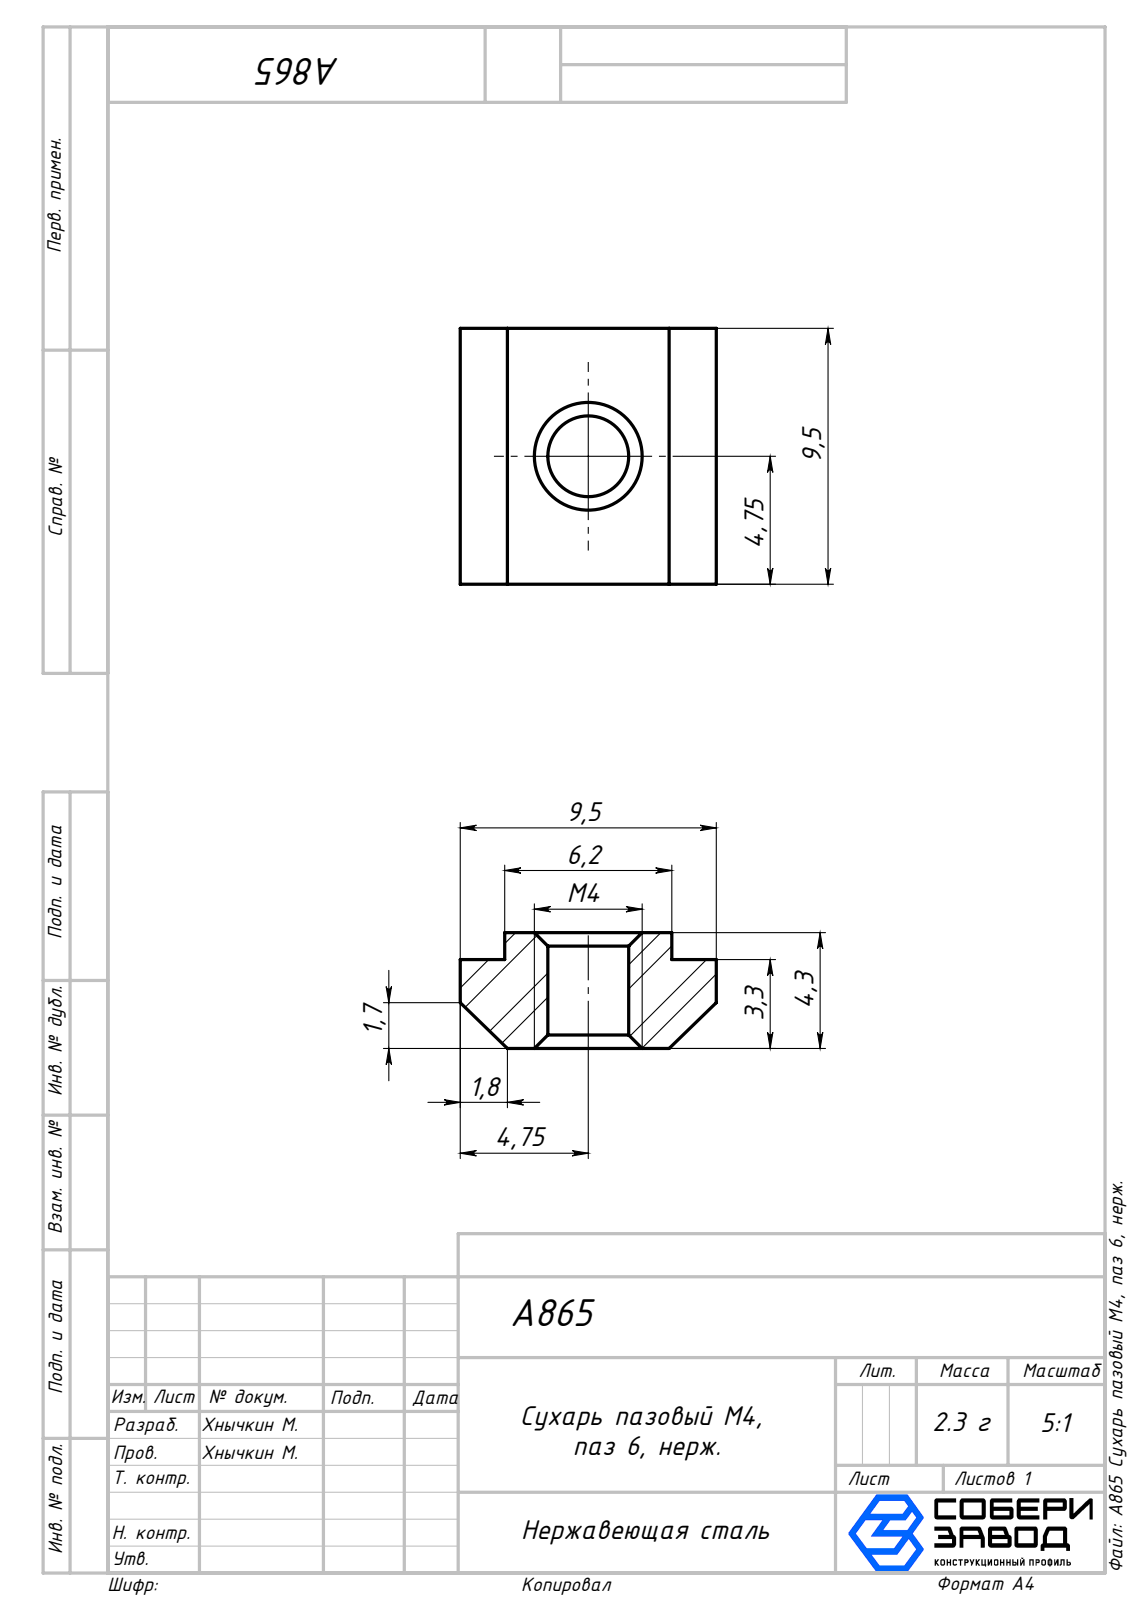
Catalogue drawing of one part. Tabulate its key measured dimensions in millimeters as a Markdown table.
| quantity | value |
| --- | --- |
| part name | A865 Сухарь пазовый М4, паз 6, нерж. |
| STEP written by | SolidWorks 2025 (AUTOMOTIVE_DESIGN) |
| units | millimeters |
| bodies | 1 solid, 18 faces (12 planar, 2 cylindrical, 4 other) |
| overall size | 9.5 × 9.5 × 4.3 |
| volume | 295 mm³ |
| surface area | 334 mm² |
| round holes (diameter × count) | 3 × 1 |
| main face-to-face distances | 9.5, 4.3, 3.3, 1, 1.65, 7.85, 6.2 |
